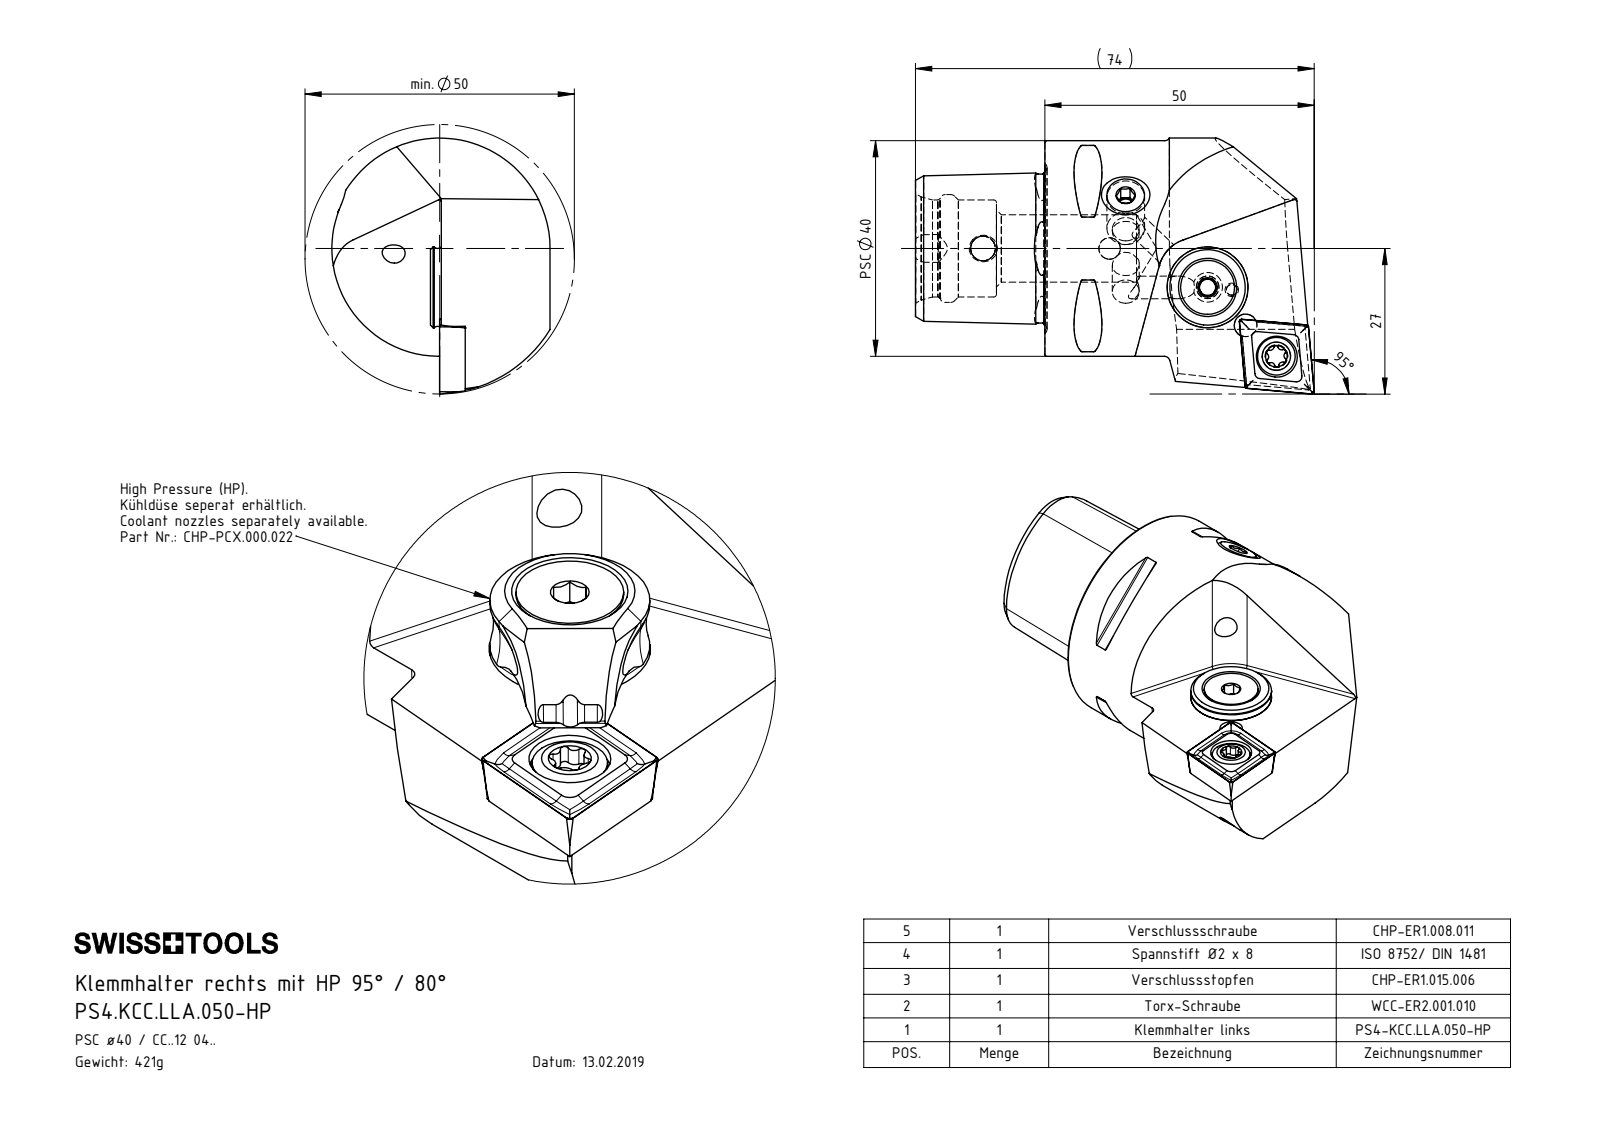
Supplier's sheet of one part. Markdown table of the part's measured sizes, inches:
| quantity | value |
| --- | --- |
| part name | WCC-ER2.001.010_A; DIN 7991 - M5x15; PS4.KCC.LLA.050-HP; PS4-KCC.LLA.050-HP_B (+6 more) |
| STEP written by | SolidWorks 2017 (AUTOMOTIVE_DESIGN) |
| units | inches |
| bodies | 8 solids, 380 faces (88 planar, 100 cylindrical, 192 other) |
| overall size | 2.913 × 1.87 × 1.594 |
| volume | 3.295 in³ |
| surface area | 24.94 in² |
| round holes (diameter × count) | 0.165 × 5, 0.047 × 1, 0.079 × 1, 0.098 × 1, 0.118 × 1, 0.157 × 1, 0.181 × 1, 0.197 × 1, 0.205 × 1, 0.217 × 1, 0.276 × 1, 0.299 × 1 |
| round bosses / shafts (diameter × count) | 0.197 × 2, 1.575 × 1, 0.591 × 1, 0.528 × 1, 0.394 × 1, 0.315 × 1, 0.276 × 1, 0.217 × 1 |
| partial cylindrical surfaces (radius × count) | 0.012 × 8, 0.015 × 6, 0.027 × 3, 0.027 × 3, 0.02 × 2, 0.118 × 1, 0.276 × 1, 0.807 × 1 |
| main face-to-face distances | 0.795, 0.618, 0.177, 0.62, 0.176, 0.945, 0.611, 1.39, 0.591, 0.87 |
| hole center spacings | 0.177, 0.278, 0.319, 0.323, 0.393, 0.584, 0.588, 0.711 |
